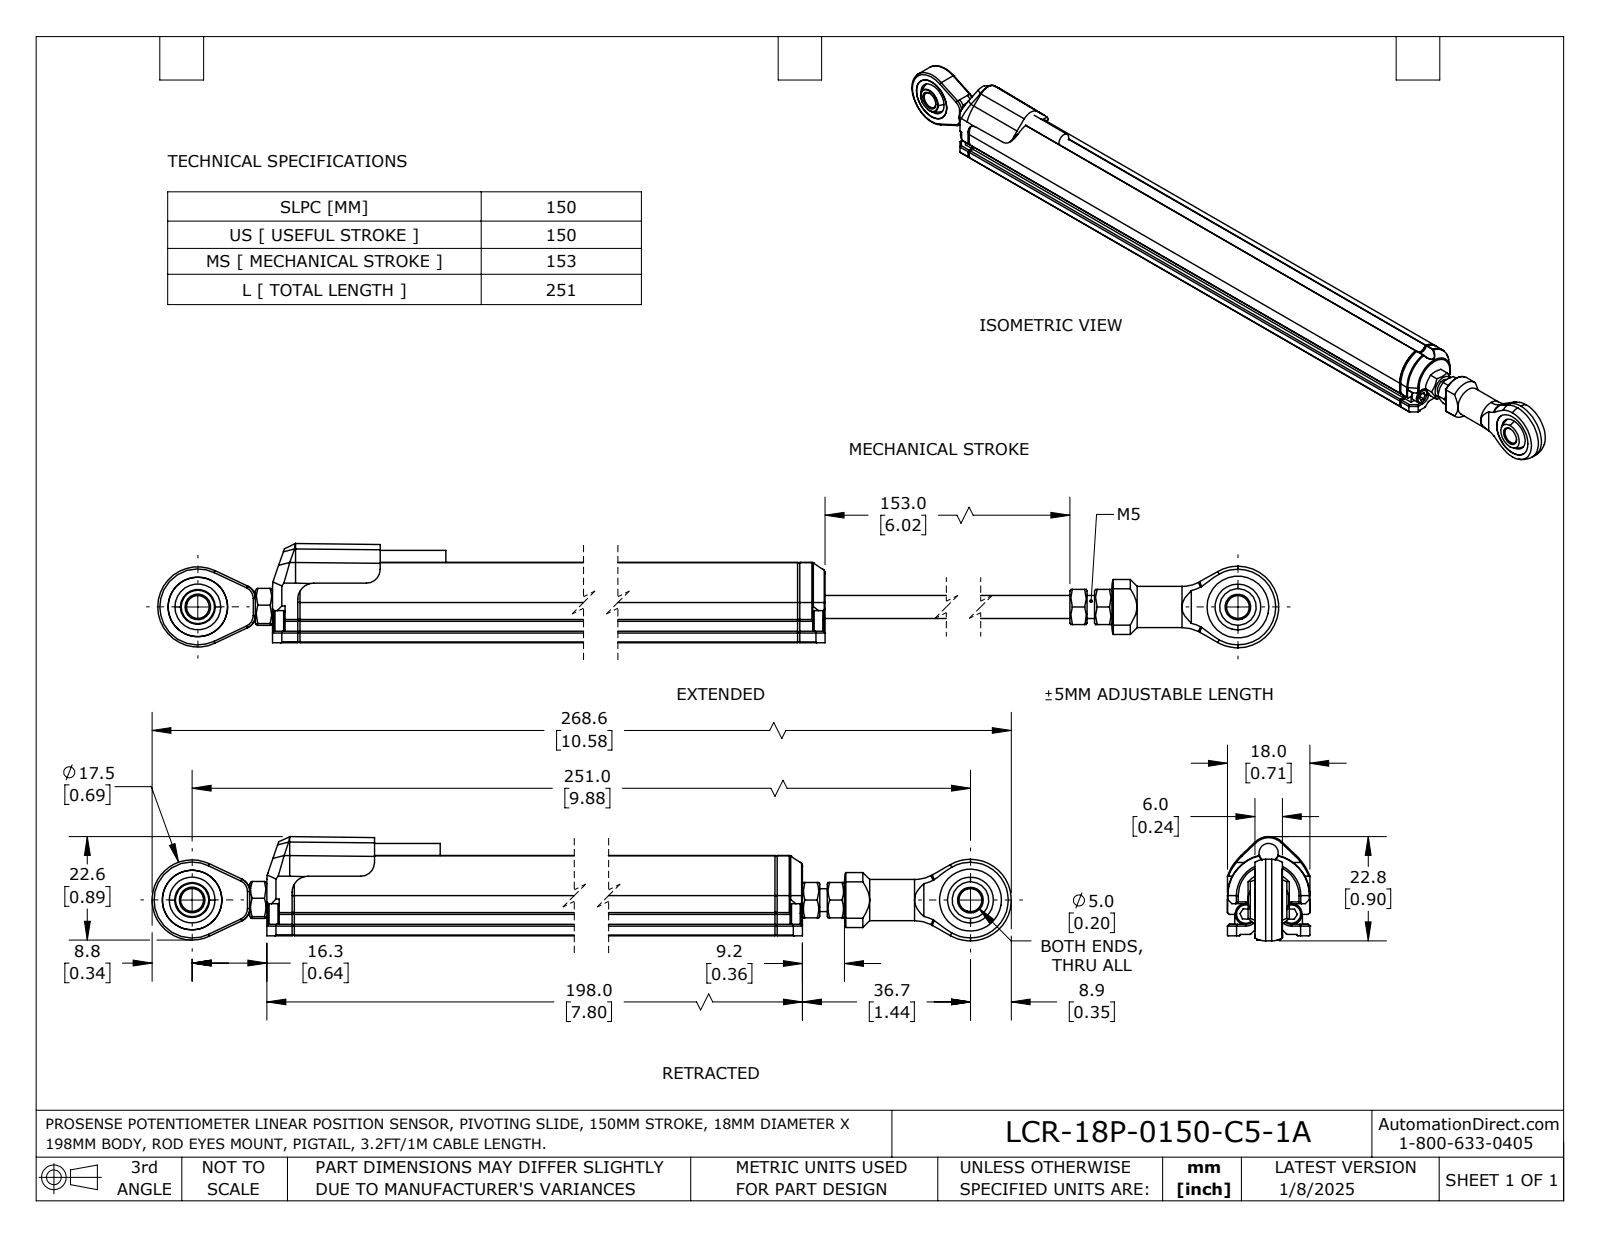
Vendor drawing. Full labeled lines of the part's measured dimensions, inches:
Part name (STEP PRODUCT): LCR-18P-0150-C5-1A
STEP written by: SolidWorks 2023 (AUTOMOTIVE_DESIGN)
Units: inches
Bodies: 20 solids, 515 faces (289 planar, 136 cylindrical, 90 other)
Overall size (bounding box): 10.577 × 0.896 × 0.709
Volume: 3.556 in³ · Surface area: 39.72 in²
Round holes (diameter × count): ⌀0.197 ×4, ⌀0.102 ×2, ⌀0.104 ×2, ⌀0.394 ×2, ⌀0.213 ×1, ⌀0.272 ×1, ⌀0.512 ×1, ⌀0.531 ×1
Round bosses / shafts (diameter × count): ⌀0.181 ×4, ⌀0.113 ×3, ⌀0.059 ×2, ⌀0.354 ×1, ⌀0.165 ×1, ⌀0.113 ×1
Partial cylindrical surfaces — rounded edges, fillets, slot ends (radius × count): R0.008 ×12, R0.004 ×10, R0.02 ×8, R0.012 ×6, R0.018 ×6, R0.016 ×4, R0.039 ×4, R0.043 ×4
Main face-to-face distances: 0.709, 0.02, 7.343, 0.236, 0.059, 0.071, 0.063, 0.646, 0.087, 0.098
Hole centre spacings: 0.231, 0.394, 0.23, 0.231, 9.882
